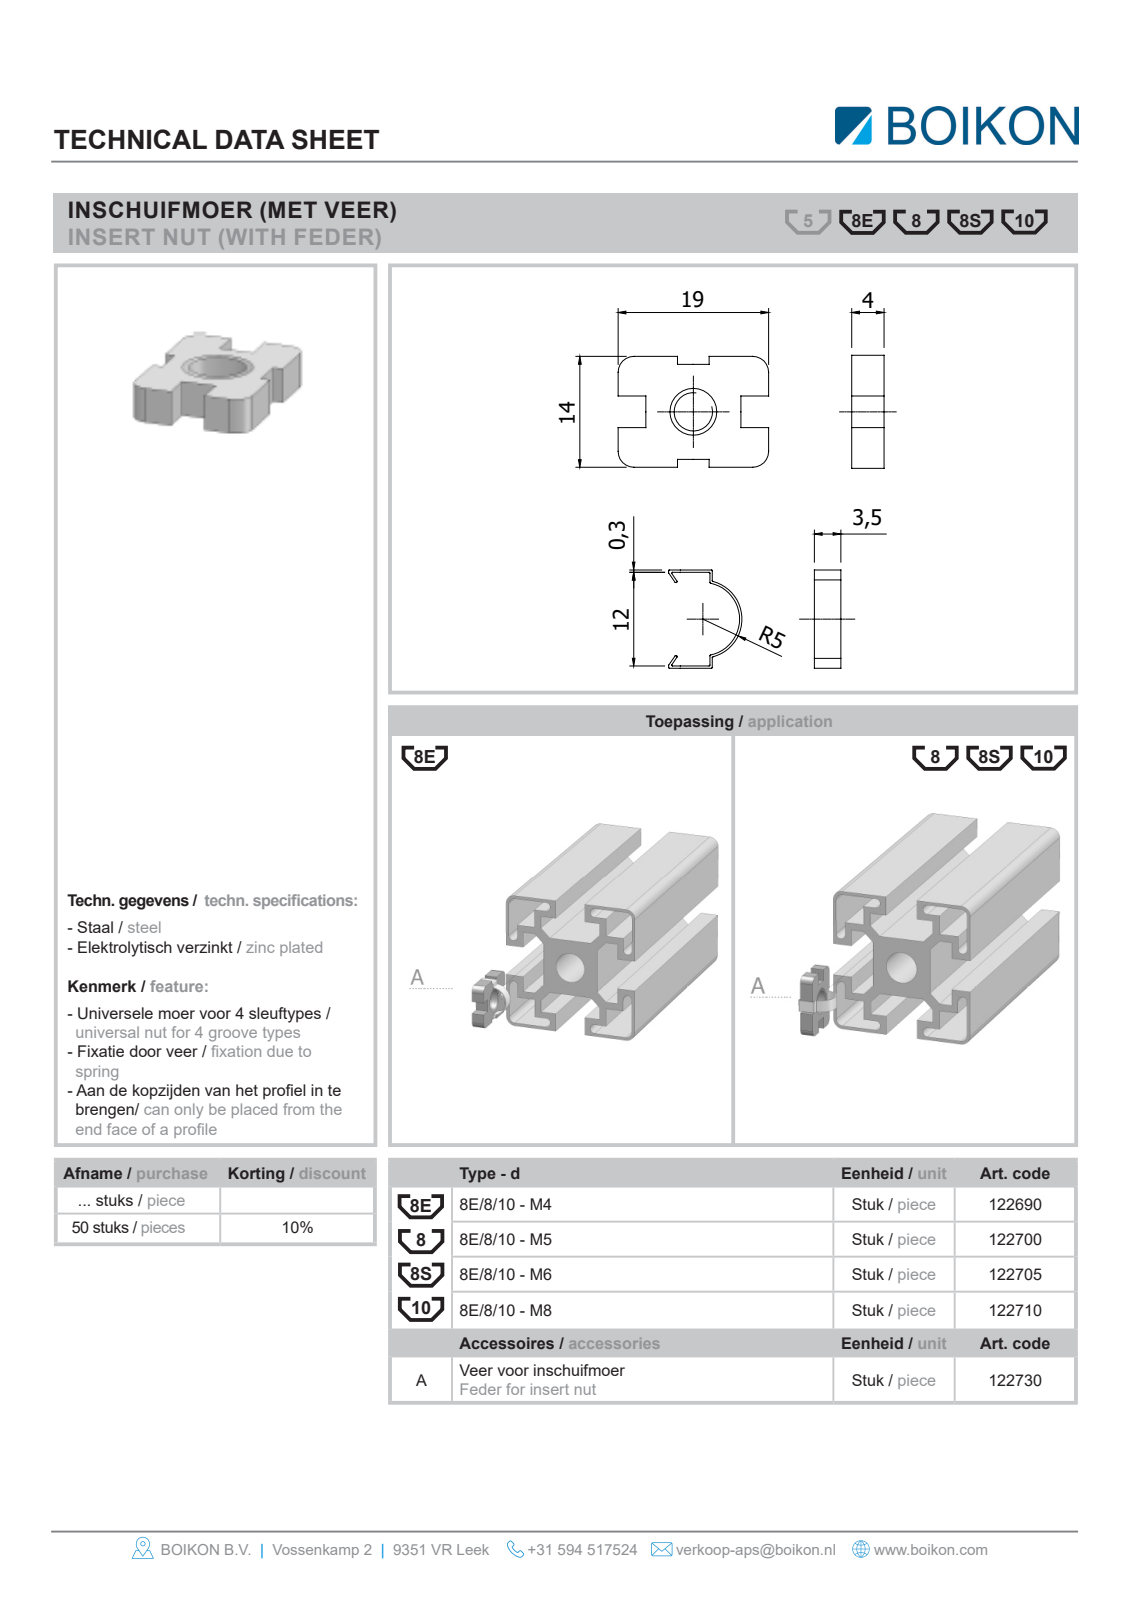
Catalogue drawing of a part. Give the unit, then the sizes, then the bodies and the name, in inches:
Units: inches
Overall size (bounding box): 0.748 × 0.551 × 0.157
Round holes (diameter × count): ⌀0.157 ×1
Main face-to-face distances: 0.157, 0.551, 0.197, 0.354, 0.154, 0.311, 0.748, 0.043, 0.508, 0.465
Volume: 0.053 in³ · Surface area: 1.27 in²
Bodies: 1 solid, 23 faces (22 planar, 1 cylindrical, 0 other)
Part name (STEP PRODUCT): Root; 122690Inschuifmoer 8E/8/10 - M4BOIKON
STEP written by: HiCAD 2013 1802.4 Build 509 (AUTOMOTIVE_DESIGN)
